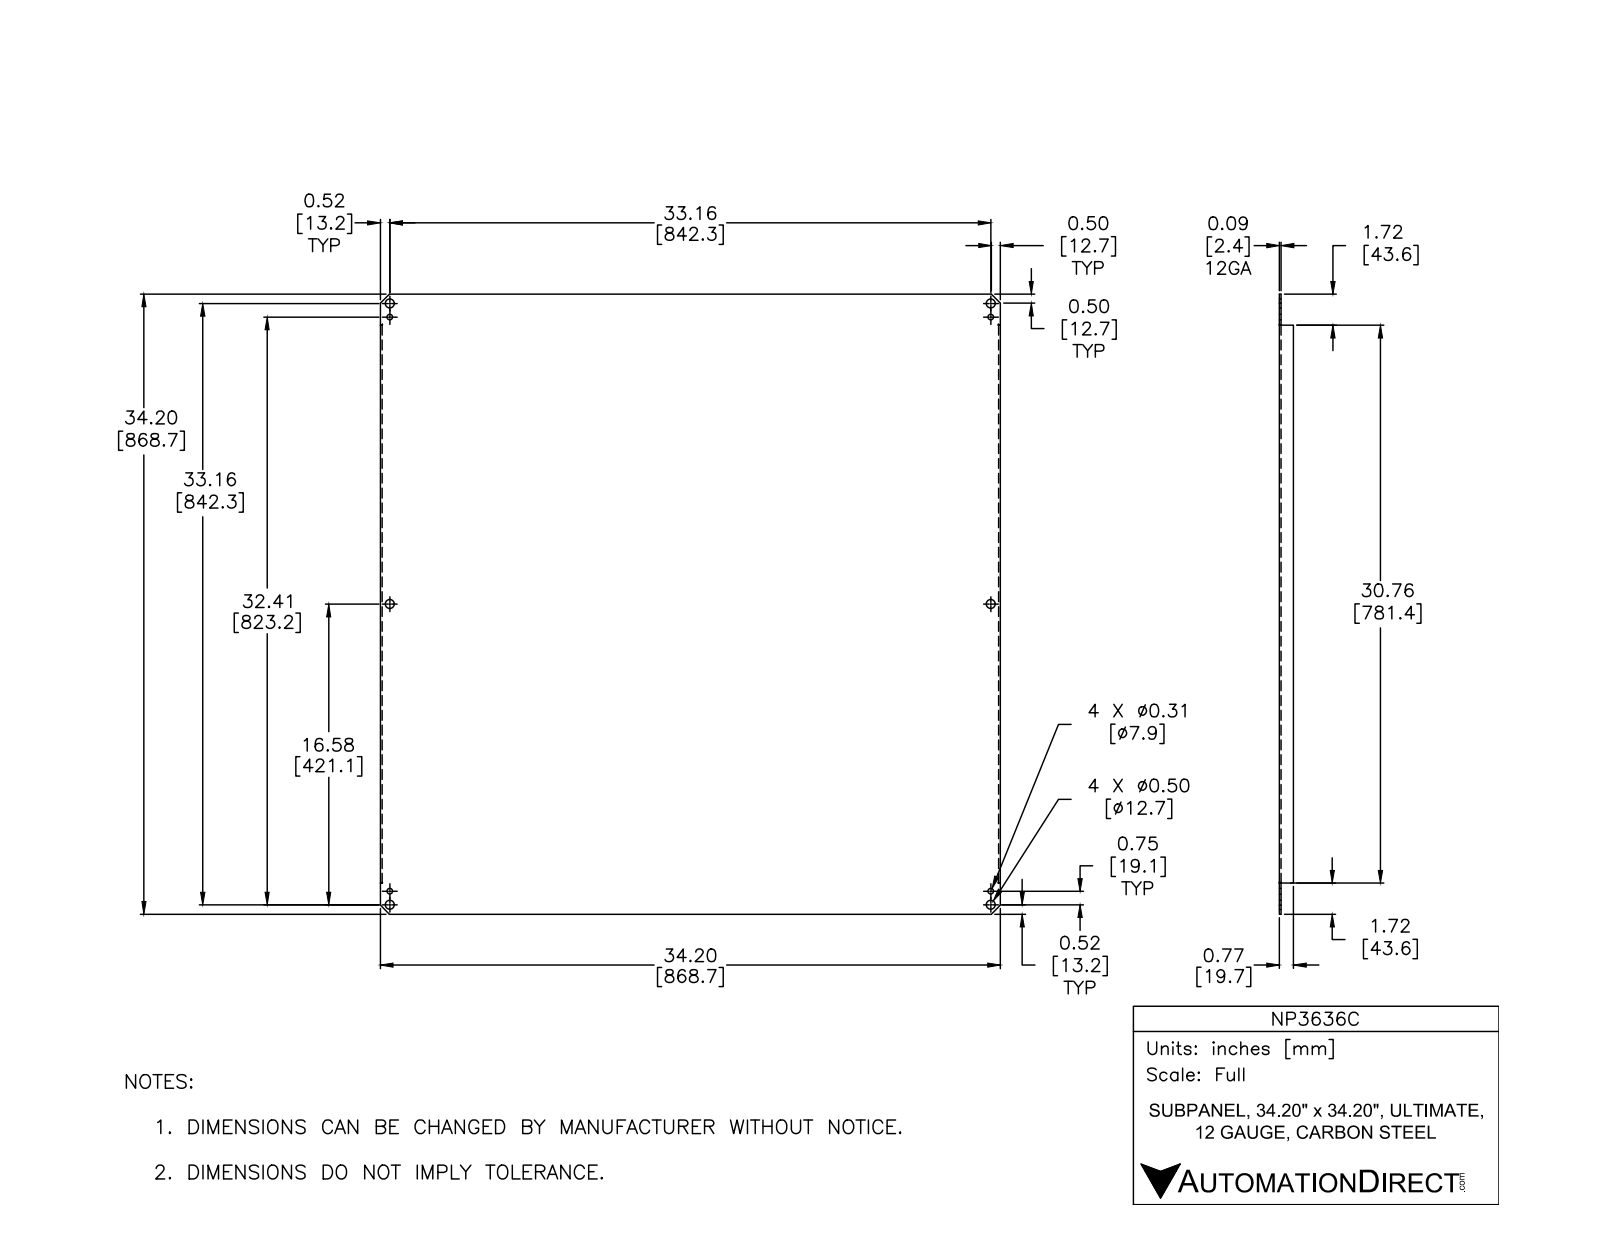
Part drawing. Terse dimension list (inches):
name: NP3636C
written by: Autodesk Inventor 2012 (AUTOMOTIVE_DESIGN)
unit: in
bodies: 1 solid, 70 faces (50 planar, 20 cylindrical, 0 other)
size: 34.2 × 34.2 × 0.774
volume: 117 in³; area: 2 510 in²
holes: 8× ⌀0.5, 4× ⌀0.313
rounds: 4× R0.016, 4× R0.109
face distances: 0.094, 34.106, 34.2, 34.013, 0.68, 0.774, 1.718, 1.624, 32.482, 32.388
hole spacings: 16.58, 33.16, 37.074, 0.75, 15.83, 16.597, 23.448, 32.41
